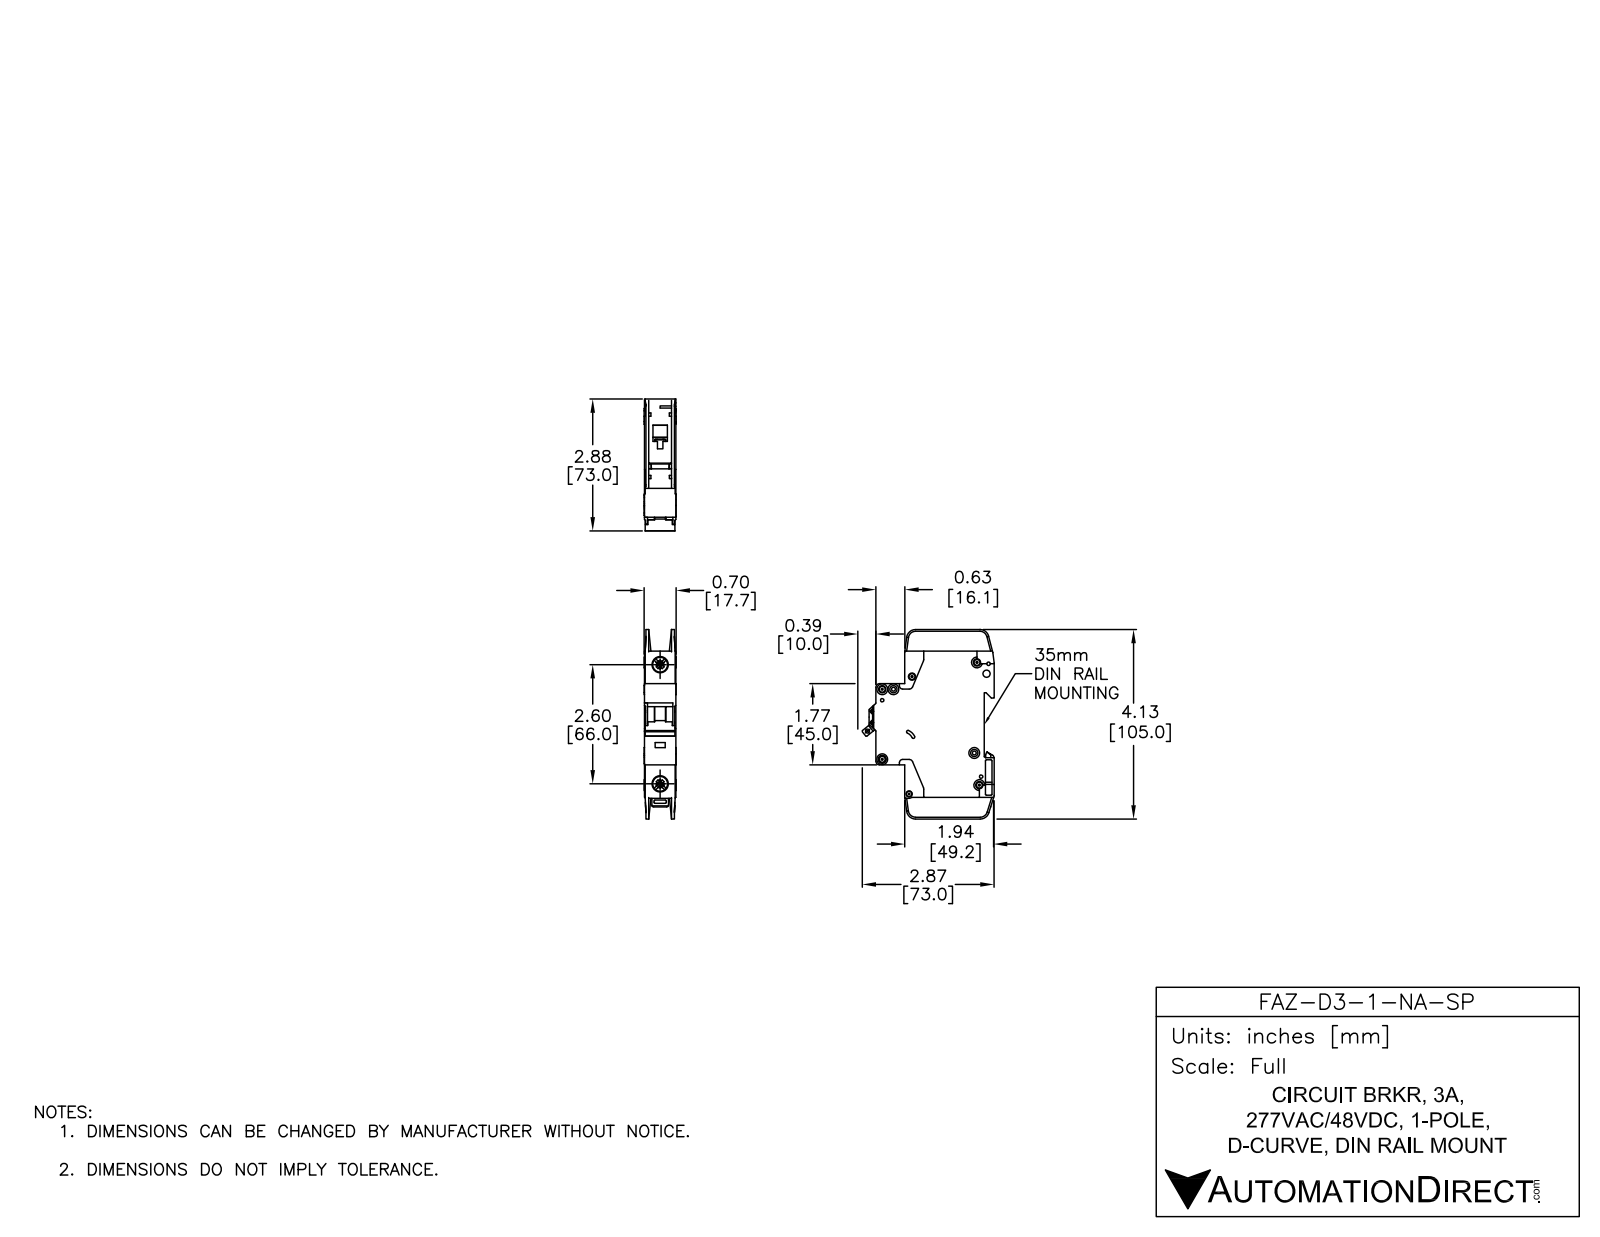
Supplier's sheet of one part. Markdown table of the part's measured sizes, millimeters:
| quantity | value |
| --- | --- |
| part name | FAZ-D3-1-NA-SP |
| STEP written by | SolidWorks 2014 (AUTOMOTIVE_DESIGN) |
| units | millimeters |
| bodies | 3 solids, 784 faces (409 planar, 263 cylindrical, 112 other) |
| overall size | 105 × 73.04 × 17.7 |
| volume | 77 695 mm³ |
| surface area | 24 740 mm² |
| round holes (diameter × count) | 3.6 × 7, 1.09 × 2, 1.5 × 2, 4 × 2, 7.15 × 2, 8.2 × 2, 1.9 × 1, 2.15 × 1, 2.2 × 1, 2.55 × 1, 3.3 × 1, 3.4 × 1 |
| round bosses / shafts (diameter × count) | 6 × 7, 2.5 × 1 |
| partial cylindrical surfaces (radius × count) | 0.25 × 29, 0.5 × 18, 1 × 10, 2 × 10, 5 × 5, 4 × 4, 1.8 × 3, 0.2 × 2 |
| main face-to-face distances | 17.5, 15.05, 0.7, 2.45, 1.75, 15.75, 13.3, 14, 12.6, 2 |
| hole center spacings | 6.2, 5.19, 6.1, 8.19, 8.56, 8.7, 11.11, 12.45 |
